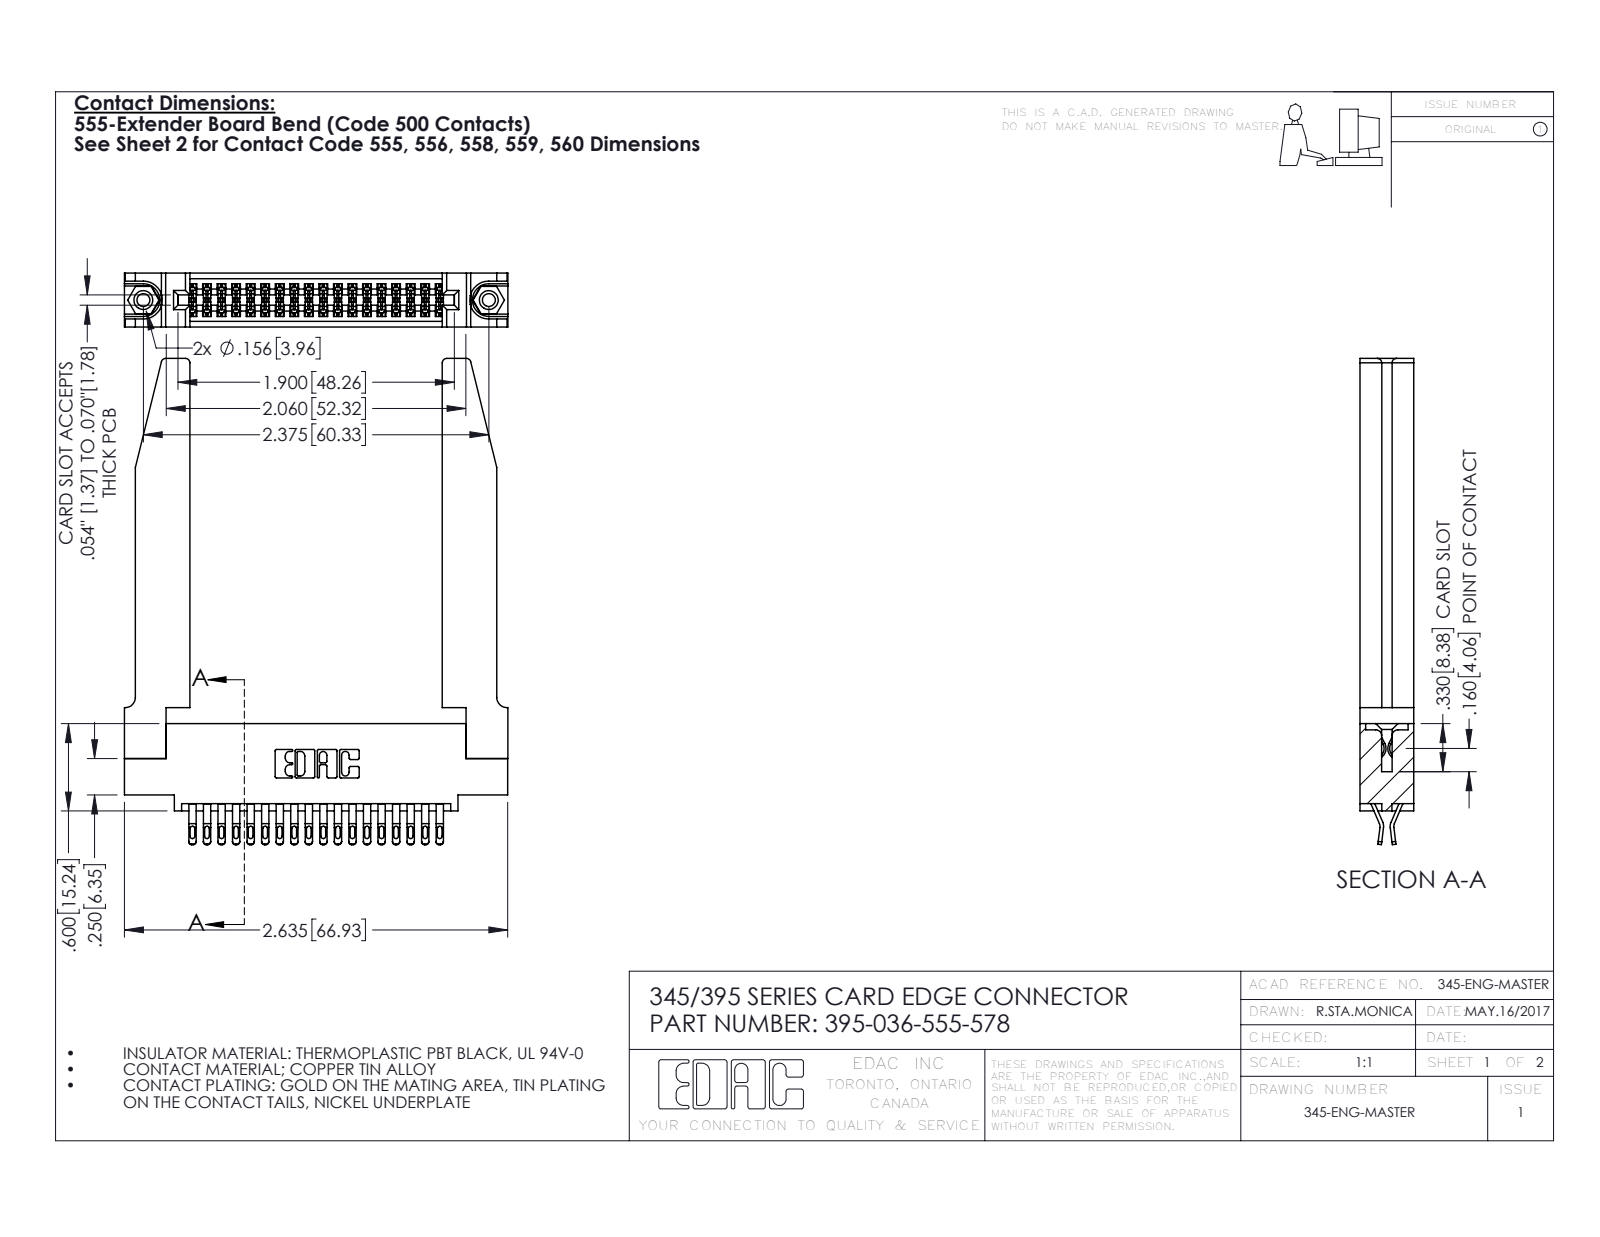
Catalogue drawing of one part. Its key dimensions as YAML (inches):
part_name: "345-220-078_345-220-078; 345-250-001_345-250-001-102; 345 Part_0.110 Offset - 0.156 Dia-TH; 345-292-001_555 Tail (+1 more)"
step_written_by: "SolidWorks 2016 (CONFIG_CONTROL_DESIGN)"
units: inches
bodies: {solids: 41, faces: 2380, planar: 1342, cylindrical: 986, other: 52}
overall_size: [3.342, 2.636, 0.37]
volume: 0.859
surface_area: 25.05
round_holes:
  - {diameter: 0.089, count: 2}
  - {diameter: 0.125, count: 2}
  - {diameter: 0.156, count: 2}
  - {diameter: 0.064, count: 1}
round_bosses_or_shafts:
  - {diameter: 0.155, count: 2}
partial_cylinders:
  - {radius: 0.016, count: 90}
  - {radius: 0.02, count: 72}
  - {radius: 0.006, count: 54}
  - {radius: 0.01, count: 22}
  - {radius: 0.03, count: 8}
  - {radius: 0.007, count: 6}
  - {radius: 0.031, count: 6}
  - {radius: 0.026, count: 3}
face_to_face_distances: [0.37, 0.072, 0.298, 0.025, 0.2, 0.15, 0.148, 0.098, 0.272, 0.225]
hole_center_spacings: [0.27, 2.141, 2.375]
